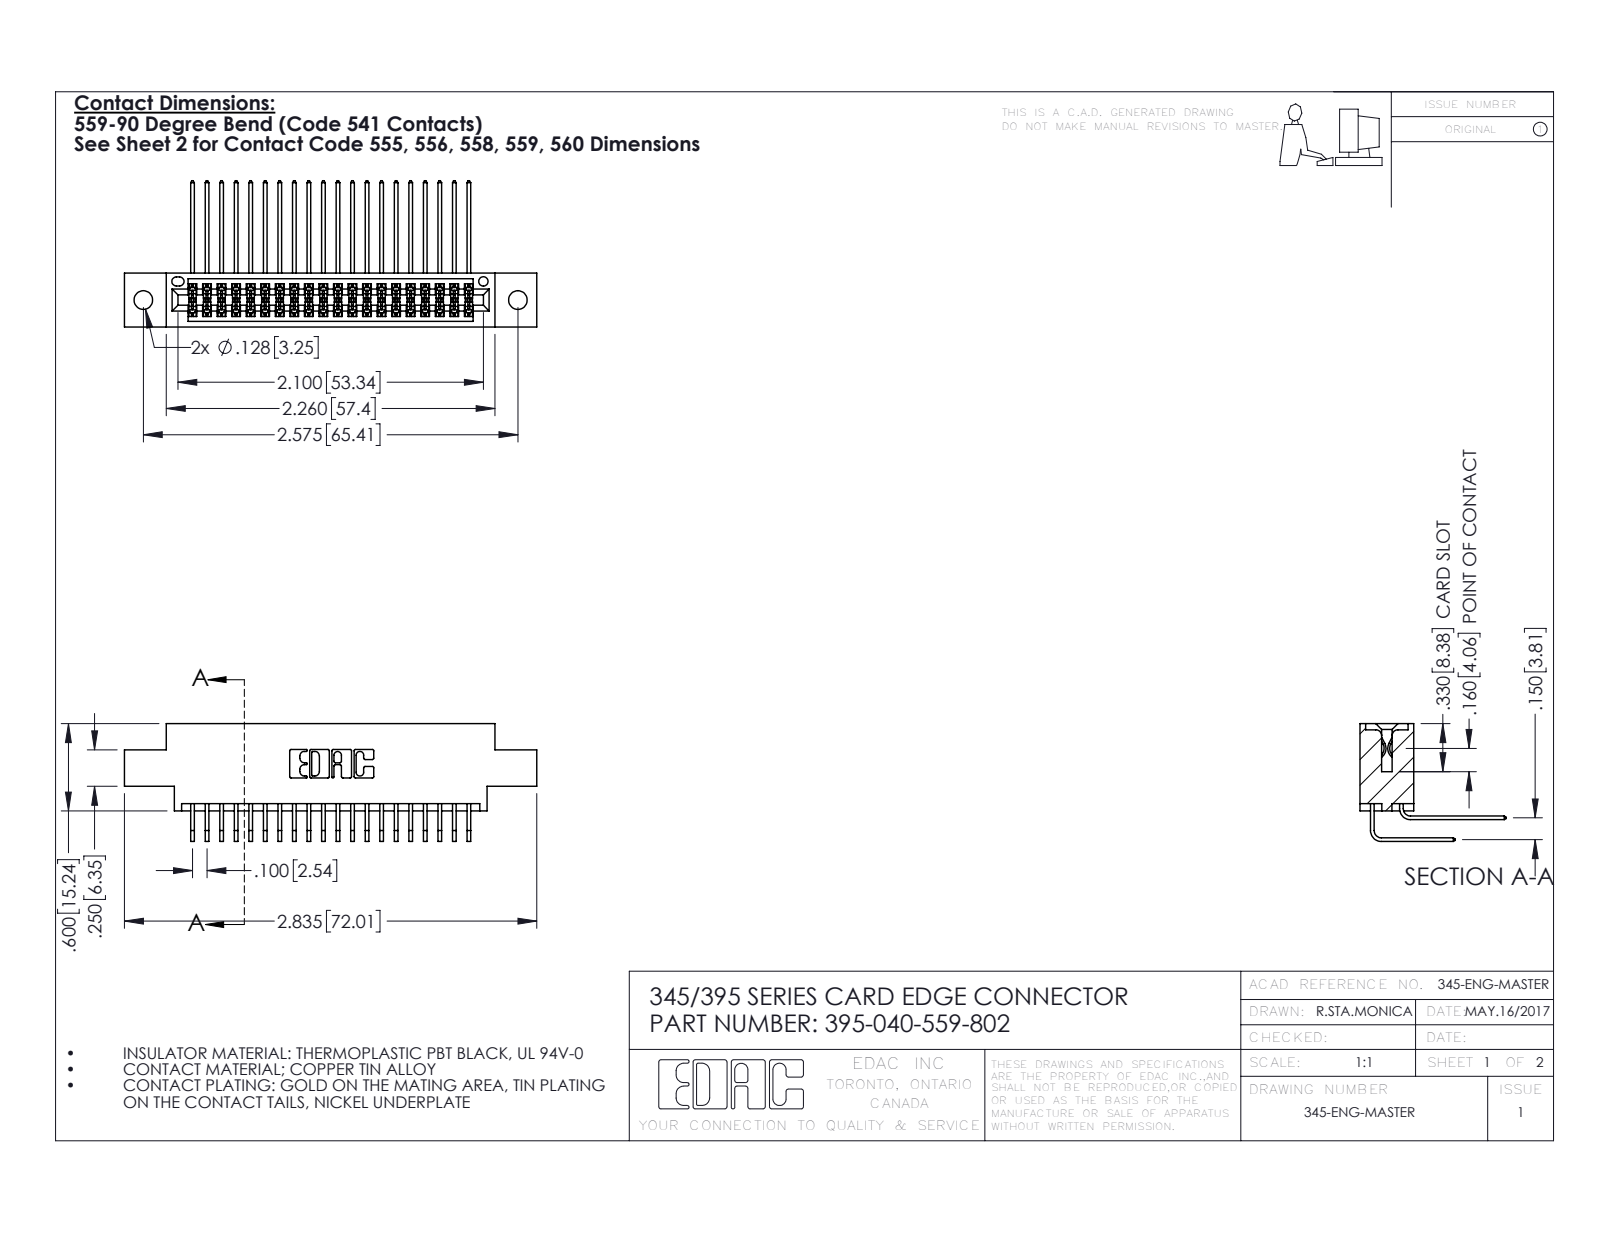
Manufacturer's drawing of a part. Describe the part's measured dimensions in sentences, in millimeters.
The part is named "395-040-559-802; 345-292-001_558 559 Tail - 1; 345 Part_0.170 Offset - 0.128 Dia; 345-292-001_559 Tail - 2". Its 3-D file was written by "SolidWorks 2016 (CONFIG_CONTROL_DESIGN)". It is 41 solids with 2210 faces: 1484 planar, 726 cylindrical and 0 other. Overall it measures 72 by 25.5 by 20.5 millimeters. Its volume is 6 870 cubic millimeters and its surface area 10 680 square millimeters. Round holes: 2 of diameter 3.3, 1 of diameter 1.6. Partial cylindrical surfaces (rounded edges, fillets, slot ends): 60 of radius 0.2, 22 of radius 0.3, 6 of radius 0.2, 6 of radius 0.8, 3 of radius 0.7, 2 of radius 0.4, 2 of radius 0.5, 2 of radius 0.6. The main face-to-face distances are 1.8, 7.6, 9.4, 5.1, 2.5, 6.9, 0.6, 3.8, 5.7, 4.4. The hole center spacings are 6.9, 59.5, 65.4.
